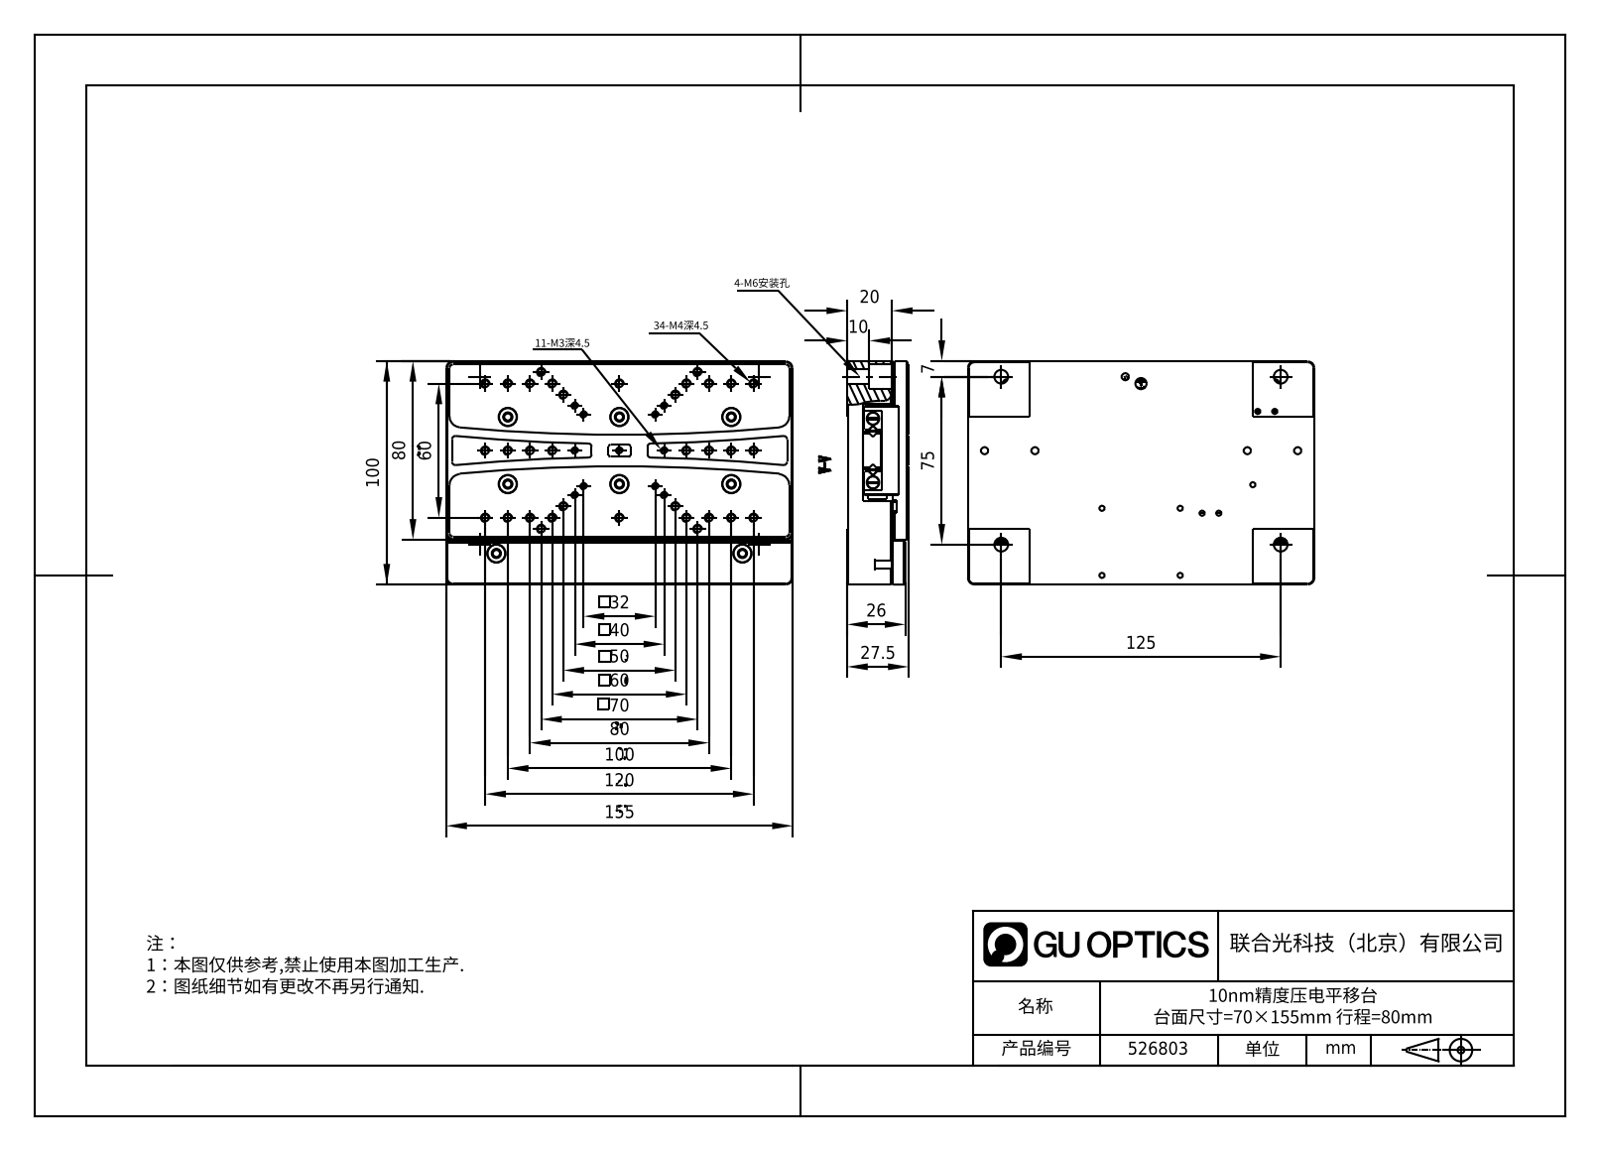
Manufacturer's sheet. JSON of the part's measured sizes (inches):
{"part_name": "526801", "step_written_by": "SolidWorks 2020 (CONFIG_CONTROL_DESIGN)", "units": "inches", "bodies": {"solids": 10, "faces": 1497, "planar": 660, "cylindrical": 565, "other": 272}, "overall_size": [6.102, 3.937, 1.083], "volume_in3": 21.08, "surface_area_in2": 217.3, "round_holes": [[0.13, 44], [0.098, 21], [0.295, 16], [0.213, 12], [0.169, 8], [0.087, 6], [0.128, 6], [0.165, 6], [0.323, 6], [0.062, 5], [0.063, 4], [0.177, 4]], "round_bosses_or_shafts": [[0.276, 12], [0.157, 12], [0.11, 1]], "partial_cylinders_radius": [[0.039, 32], [0.059, 29], [0.02, 22], [0.118, 15], [0.079, 12], [0.069, 10], [0.122, 10], [0.008, 8]], "face_to_face_distances": [0.256, 0.295, 0.02, 0.177, 0.63, 0.807, 0.118, 0.787, 0.886, 1.063], "hole_center_spacings": [0.984, 1.969, 0.493, 1.25, 1.49, 2.953, 1.477, 1.871]}
